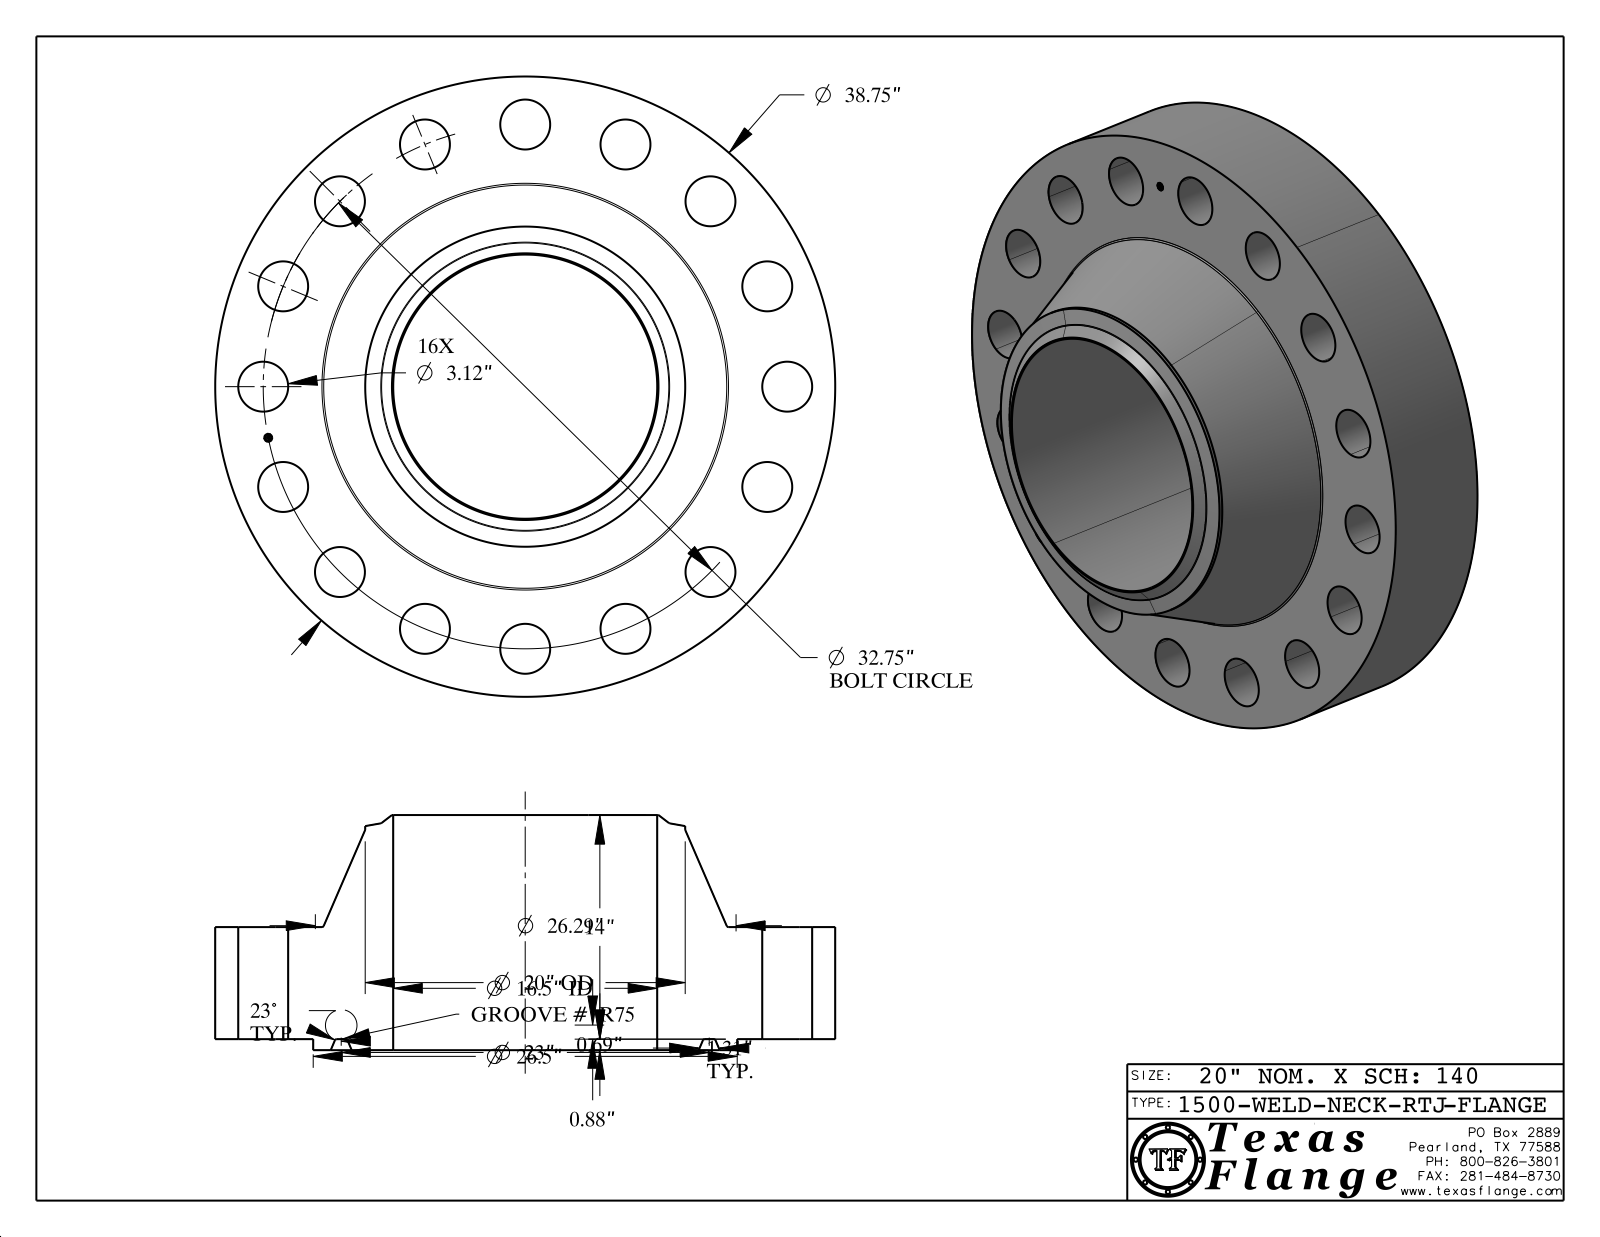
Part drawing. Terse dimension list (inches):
name: 1500-WELD-NECK-RTJ
written by: CATIA V5 STEP AP214 (AUTOMOTIVE_DESIGN)
unit: in
bodies: 1 solid, 449 faces (371 planar, 60 cylindrical, 18 other)
size: 38.75 × 38.75 × 14.688
volume: 7 285 in³; area: 4 826 in²
holes: 16× ⌀3.12, 1× ⌀0.495, 1× ⌀16.5
bosses: 8× ⌀0.03, 1× ⌀38.75, 1× ⌀26.5, 1× ⌀20, 1× ⌀0.39
face distances: 7, 0.688, 7.688, 14.688, 14, 7.673, 6.985, 0.015, 7.015, 0.148
hole spacings: 18.195, 16.375, 12.533, 23.157, 30.257, 6.389, 6.389, 27.23
